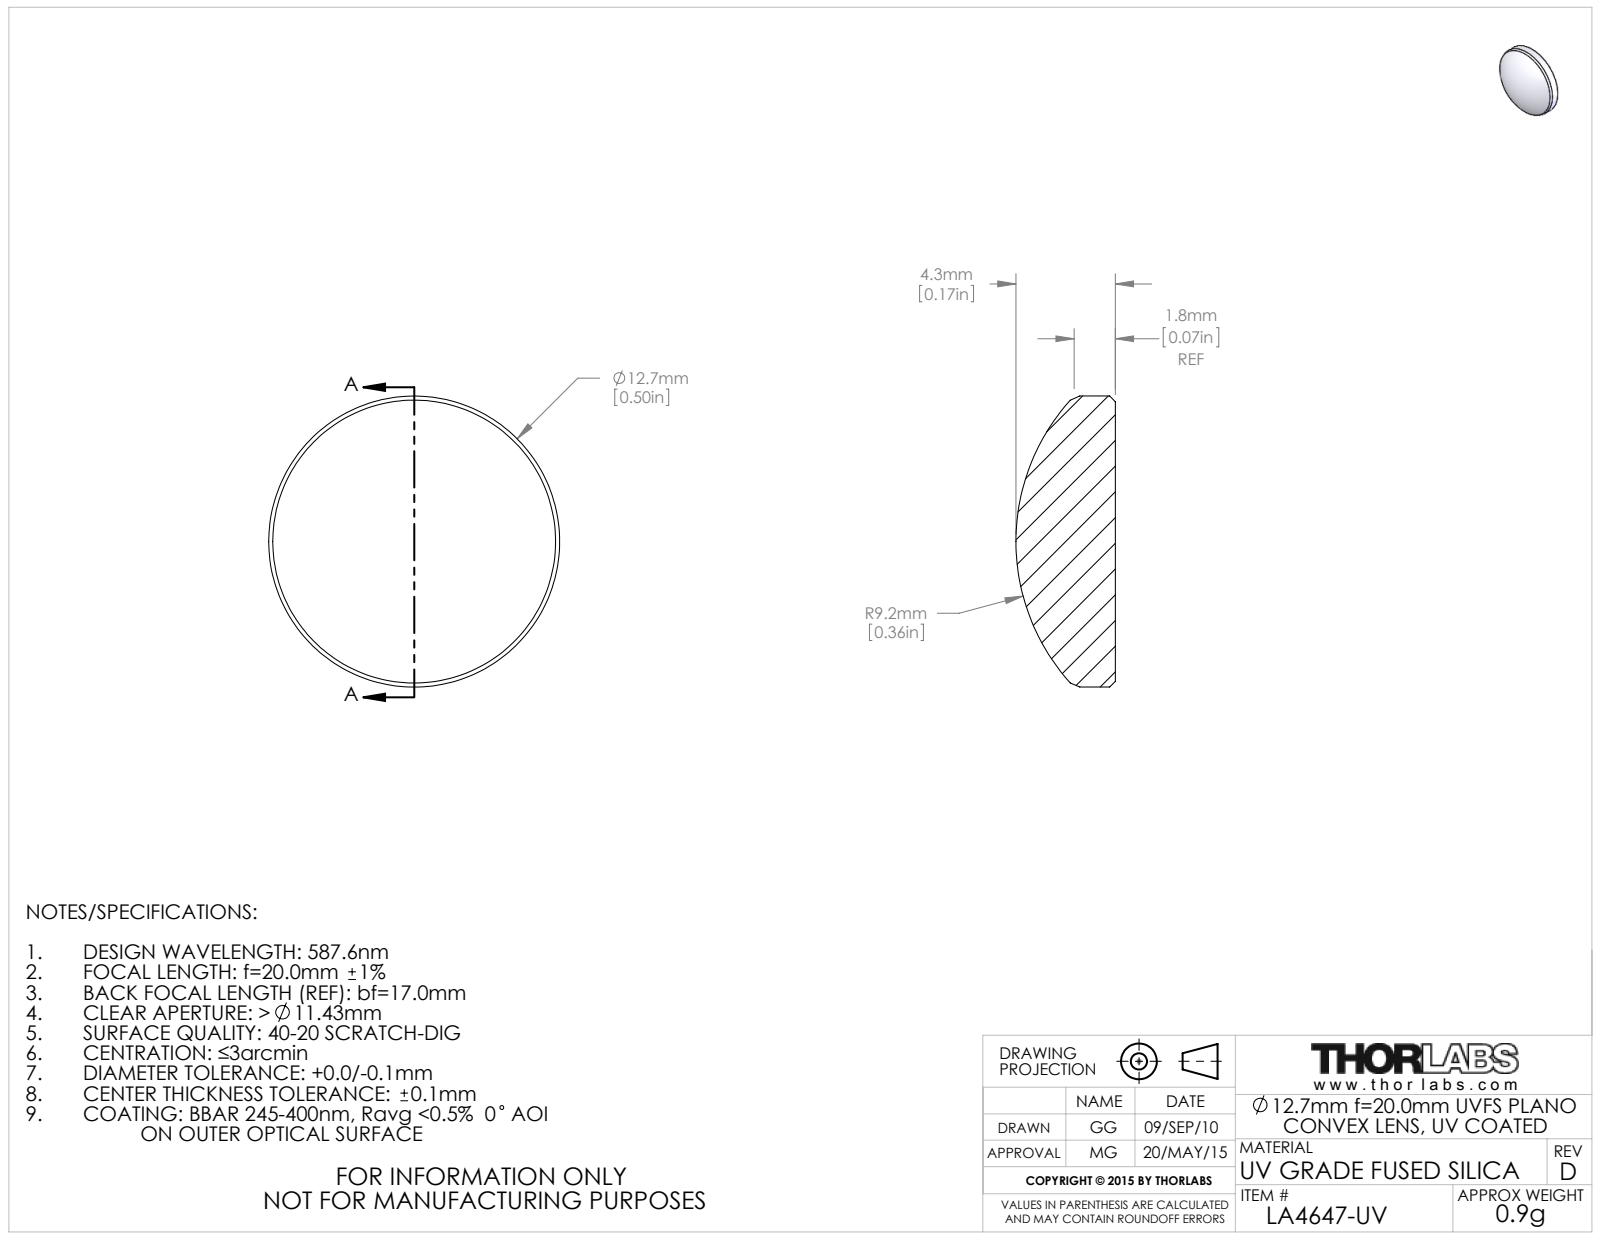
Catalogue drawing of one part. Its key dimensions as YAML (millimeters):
part_name: "4272-E0W"
step_written_by: "SolidWorks 2014 (CONFIG_CONTROL_DESIGN)"
units: millimeters
bodies: {solids: 1, faces: 9, planar: 1, cylindrical: 2, other: 6}
overall_size: [12.7, 12.7, 4.34]
volume: 395
surface_area: 338
round_bosses_or_shafts:
  - {diameter: 12.7, count: 1}
